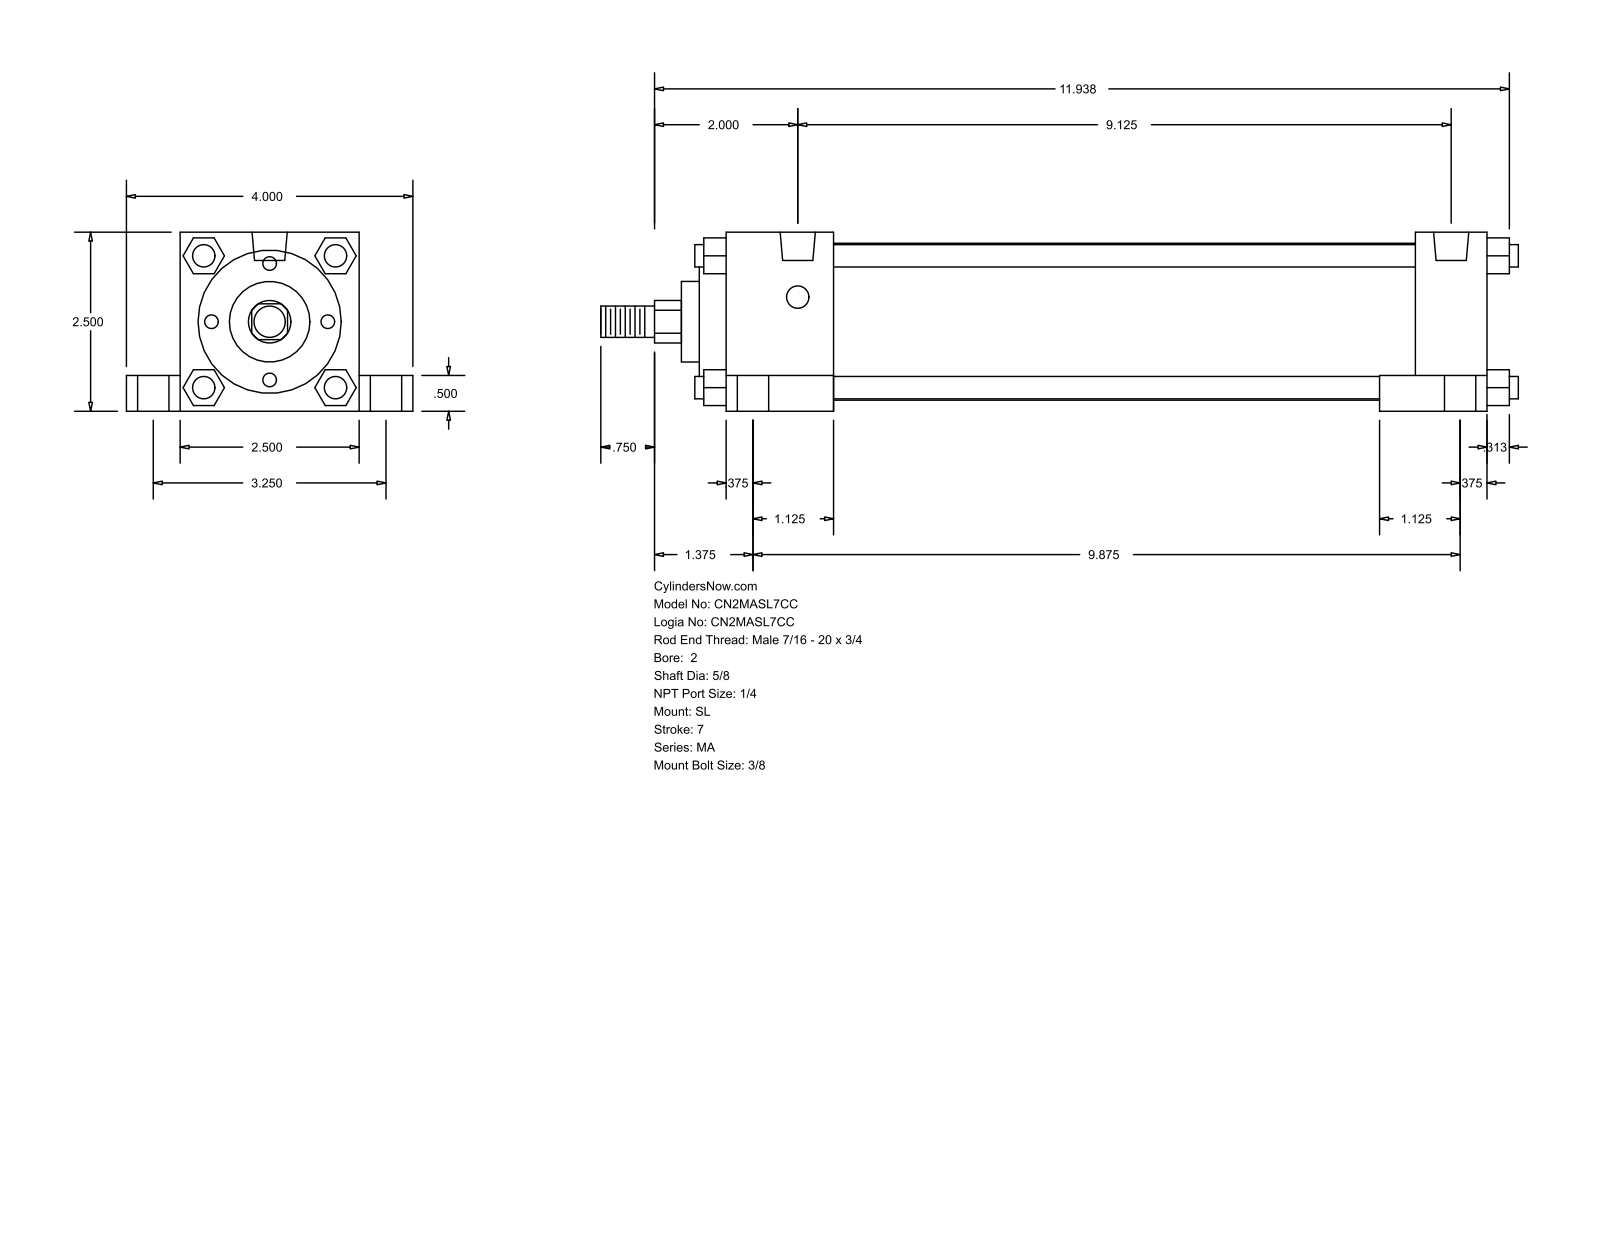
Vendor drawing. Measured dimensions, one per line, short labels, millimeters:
name: MA_SL__0200_0.625
written by: GSSL Pune (CONFIG_CONTROL_DESIGN)
unit: mm
bodies: 0 solids, 150 faces (113 planar, 37 cylindrical, 0 other)
size: 325.44 × 101.6 × 63.5
holes: 4× ⌀7.94, 4× ⌀11.11, 4× ⌀17.46, 2× ⌀12.49
bosses: 4× ⌀7.94, 1× ⌀55.63, 1× ⌀50.8, 1× ⌀28.57, 1× ⌀15.88, 1× ⌀11.11
rounds: 1× R7.54
face distances: 63.5, 12.7, 9.52, 19.05, 82.55, 38.1, 50.8, 269.87, 231.77, 244.48
hole spacings: 41.39, 44.22, 82.54, 231.77, 238.55, 250.83, 251.07, 264.06
